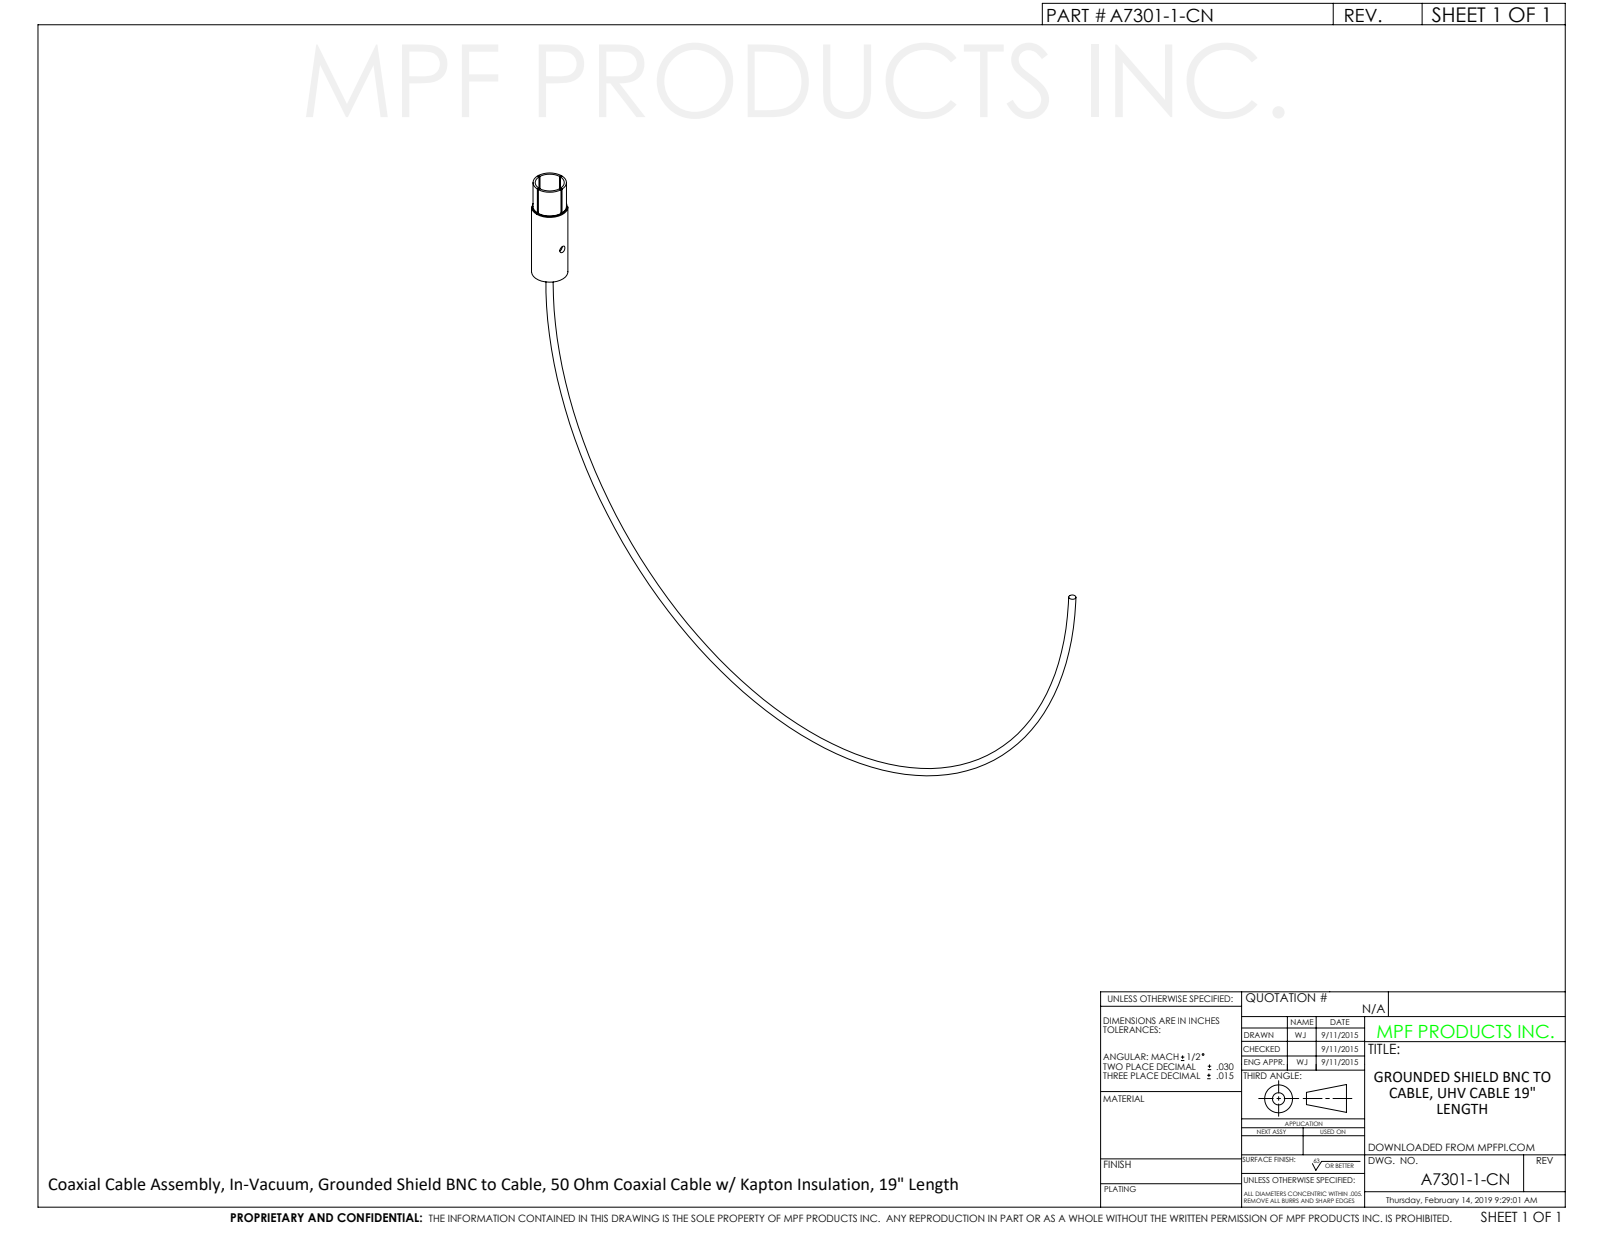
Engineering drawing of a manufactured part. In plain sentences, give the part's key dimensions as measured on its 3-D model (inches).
The part is named "A7301-1-CN". Its 3-D file was written by "SolidWorks 2018 (CONFIG_CONTROL_DESIGN)". It is 1 solid with 34 faces: 17 planar, 12 cylindrical and 5 other. Overall it measures 10.462 by 6.833 by 0.5 inches. Its volume is 0.242 cubic inches and its surface area 9.439 square inches. Round holes: 2 of diameter 0.1, 1 of diameter 0.4. Round bosses or shafts: 1 of diameter 0.5, 1 of diameter 0.46. The main face-to-face distances are 0.2, 0.02, 1.5, 1.3, 1.1, 0.9, 0.4.
